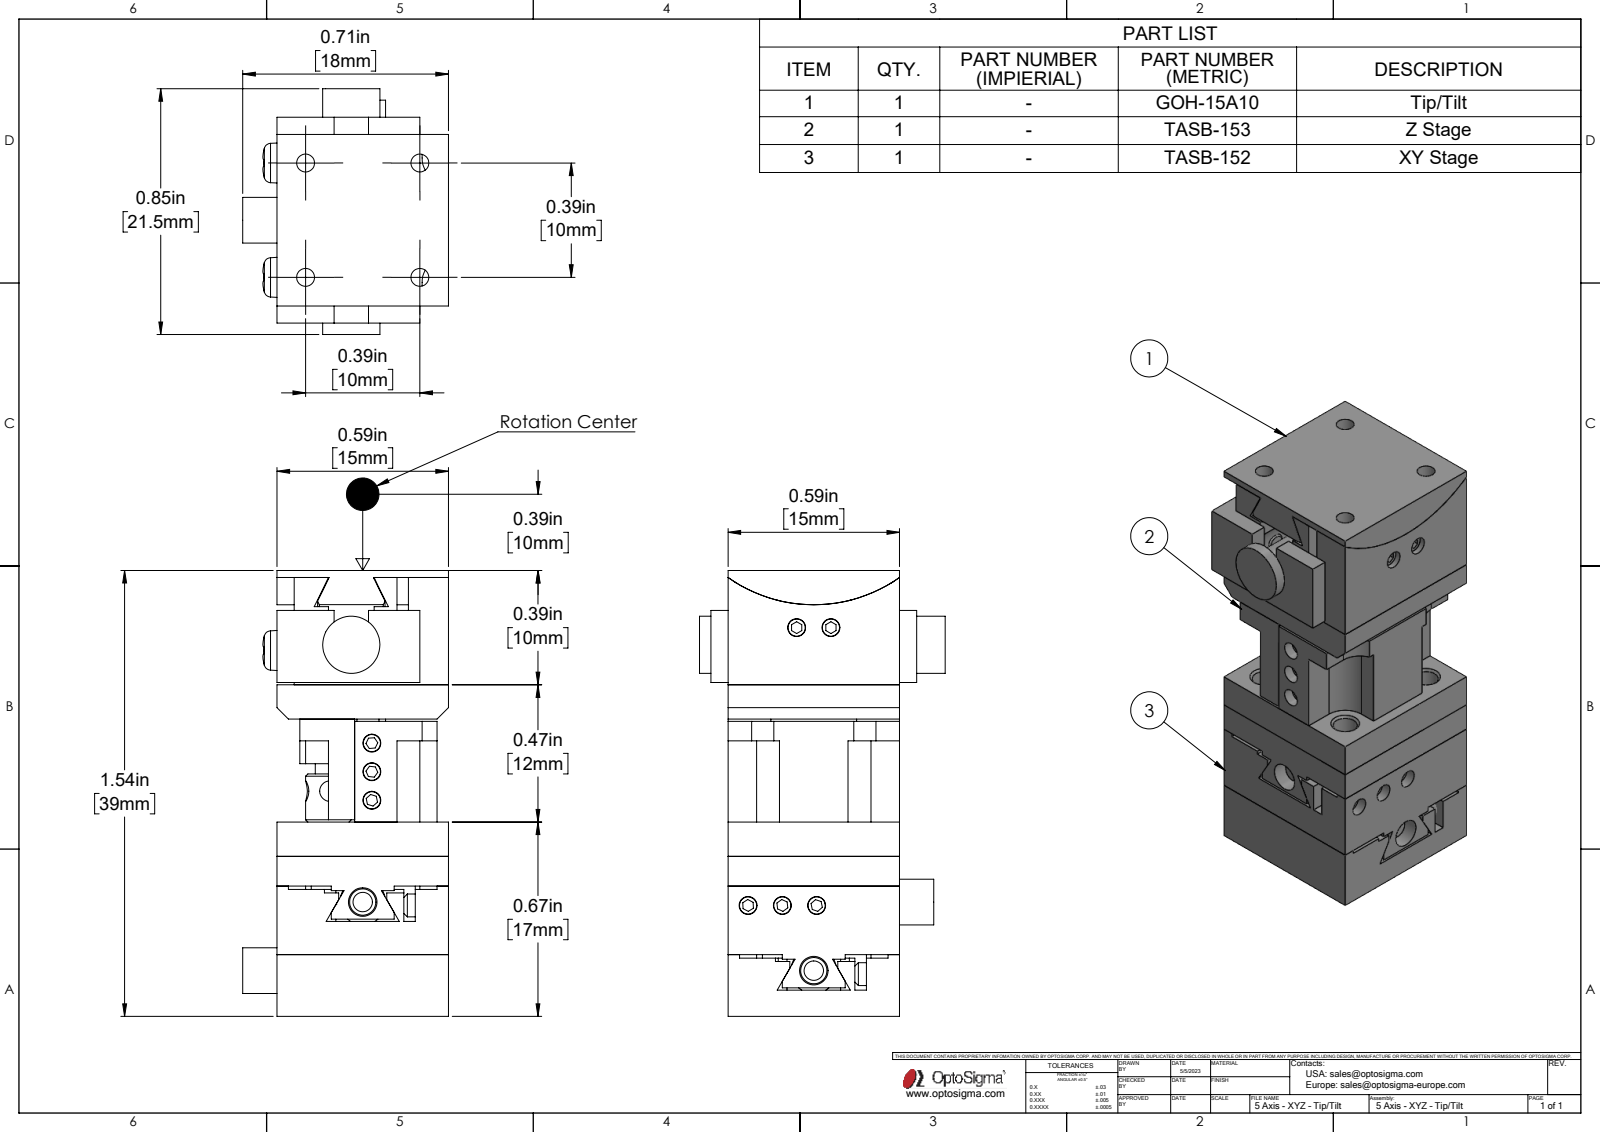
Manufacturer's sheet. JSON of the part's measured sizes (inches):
{"part_name": "HS_M2×2^TASB-153-C1-P01_TASB-153(2)_TASB-153; TASB-152-C1-P01^TASB-152(2)_TASB-152; TASB-152-C1-P02^TASB-152(2)_TASB-152; TASB-151-03^TASB-152-C1-P01_TASB-152(2)_TASB-152 (+8 more)", "step_written_by": "SolidWorks 2023 (AUTOMOTIVE_DESIGN)", "units": "inches", "bodies": {"solids": 25, "faces": 848, "planar": 410, "cylindrical": 164, "other": 274}, "overall_size": [1.535, 0.846, 0.709], "volume_in3": 0.428, "surface_area_in2": 14.68, "round_holes": [[0.071, 2]], "round_bosses_or_shafts": [[0.079, 20], [0.157, 3], [0.091, 3], [0.197, 1], [0.118, 1]], "partial_cylinders_radius": [[0.031, 24], [0.039, 11], [0.059, 8], [0.079, 6], [0.089, 2], [0.104, 2], [0.049, 1], [0.098, 1]], "face_to_face_distances": [0.591, 0.118, 0.472, 0.236, 0.114, 0.177, 0.102, 0.098, 0.354, 0.512]}
